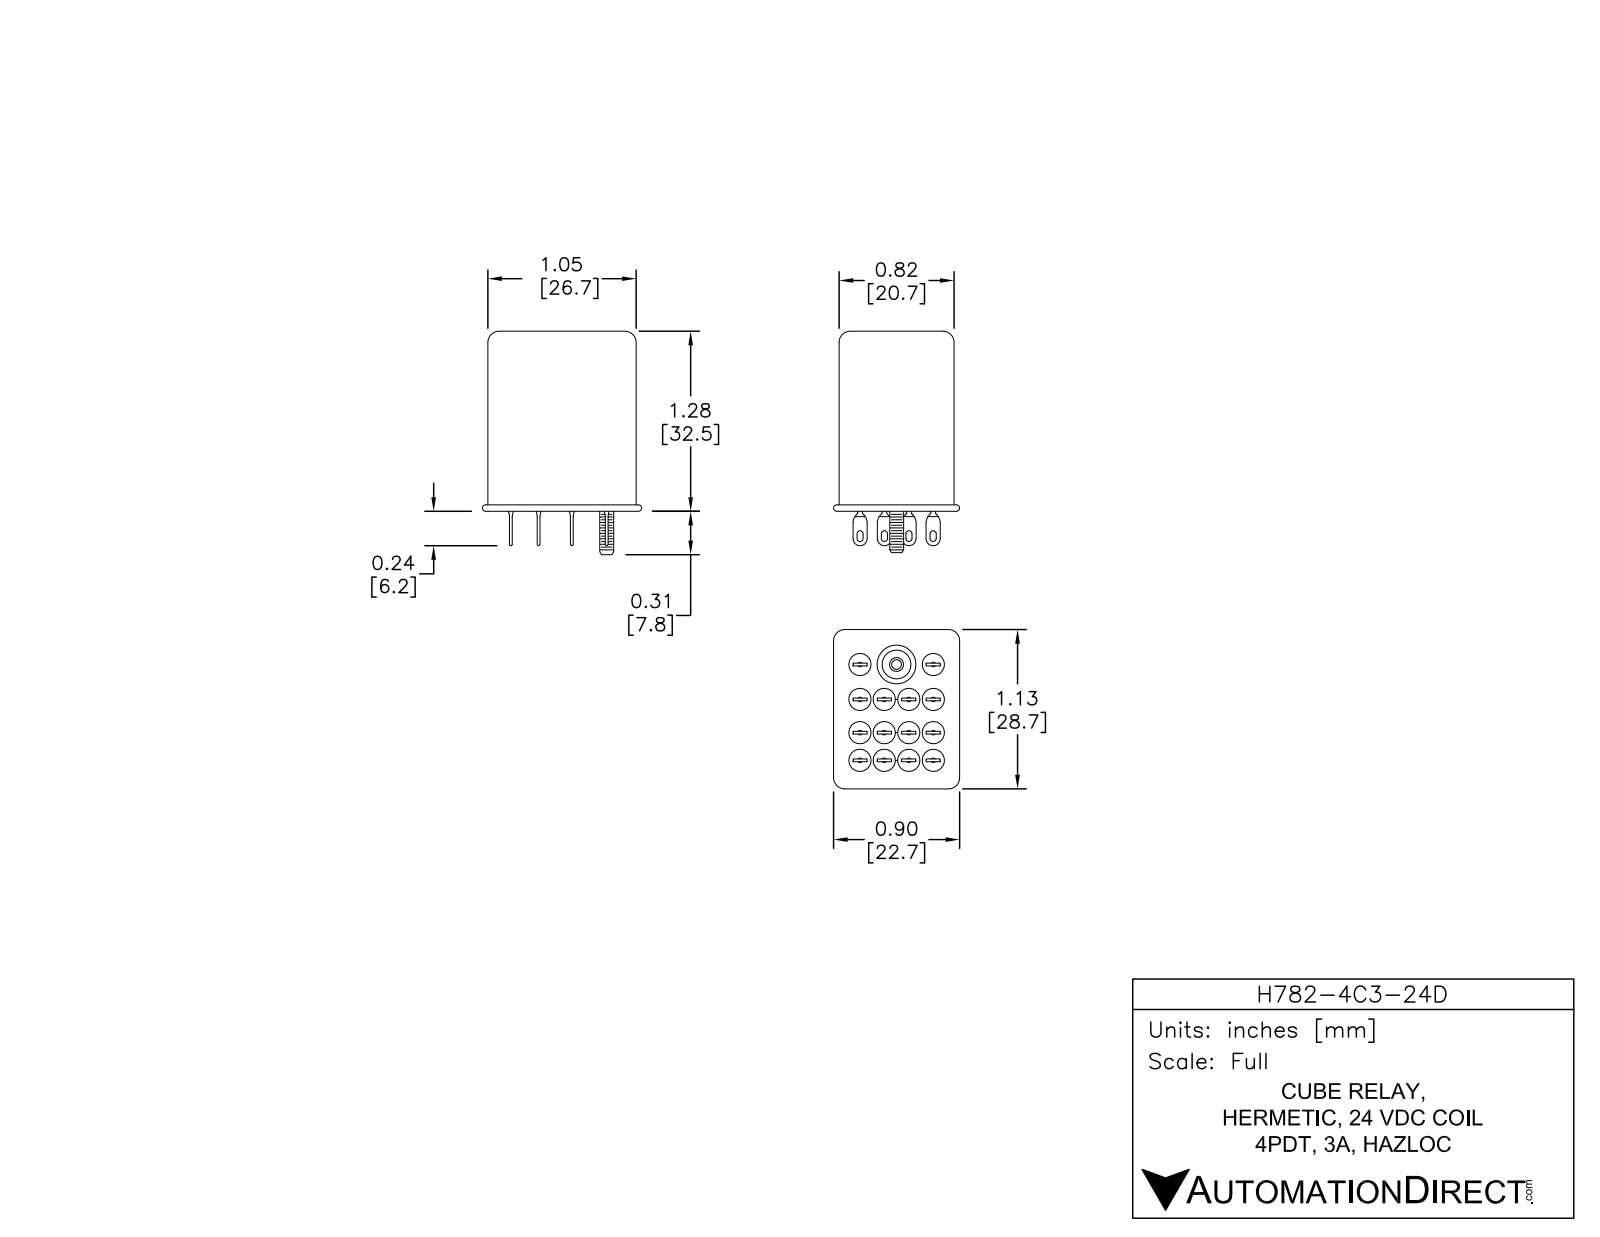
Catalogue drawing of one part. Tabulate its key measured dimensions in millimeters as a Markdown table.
| quantity | value |
| --- | --- |
| part name | H782-4C3-24D |
| STEP written by | SolidWorks 2013 (AUTOMOTIVE_DESIGN) |
| units | millimeters |
| bodies | 2 solids, 408 faces (186 planar, 178 cylindrical, 44 other) |
| overall size | 35.12 × 28.8 × 22.9 |
| volume | 15 264 mm³ |
| surface area | 4 133 mm² |
| round holes (diameter × count) | 6 × 1 |
| round bosses / shafts (diameter × count) | 3.15 × 14, 2.4 × 1 |
| partial cylindrical surfaces (radius × count) | 0.1 × 56, 0.5 × 36, 0.2 × 8, 2 × 4 |
| main face-to-face distances | 20.5, 27.6, 26.5, 27.62, 5.2, 0.4, 10.4, 10, 4.8, 5.6 |
